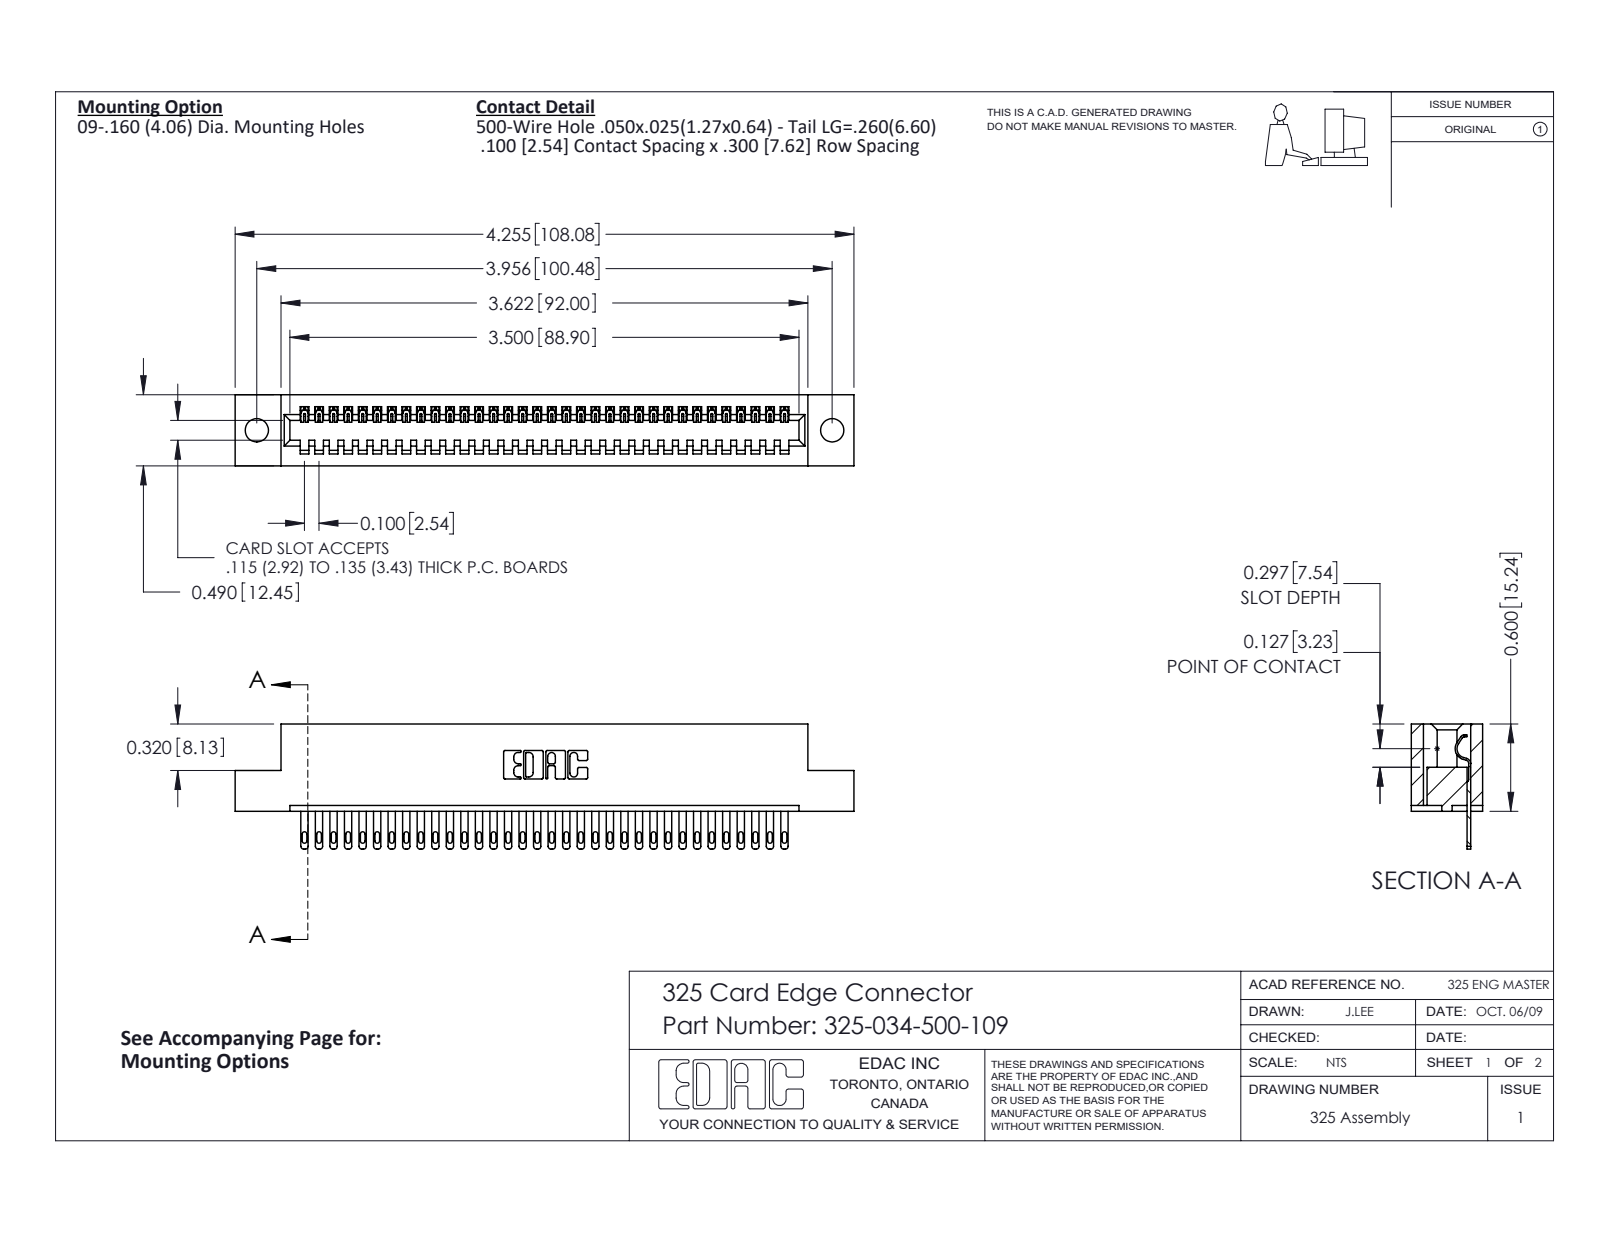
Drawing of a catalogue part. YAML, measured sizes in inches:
part_name: "325 Part_.160 TH; 325-292-001_325-293-100; 325-034-500-109"
step_written_by: "SolidWorks 2016 (CONFIG_CONTROL_DESIGN)"
units: inches
bodies: {solids: 35, faces: 1950, planar: 1294, cylindrical: 656, other: 0}
overall_size: [4.255, 0.86, 0.49]
volume: 0.821
surface_area: 22.52
round_holes:
  - {diameter: 0.16, count: 2}
partial_cylinders:
  - {radius: 0.006, count: 68}
  - {radius: 0.016, count: 68}
  - {radius: 0.02, count: 68}
  - {radius: 0.01, count: 22}
  - {radius: 0.007, count: 6}
  - {radius: 0.031, count: 6}
  - {radius: 0.026, count: 3}
  - {radius: 0.014, count: 1}
face_to_face_distances: [0.083, 0.407, 0.49, 0.3, 0.107, 0.383, 0.025, 0.325, 0.04, 0.56]
hole_center_spacings: [3.956]
